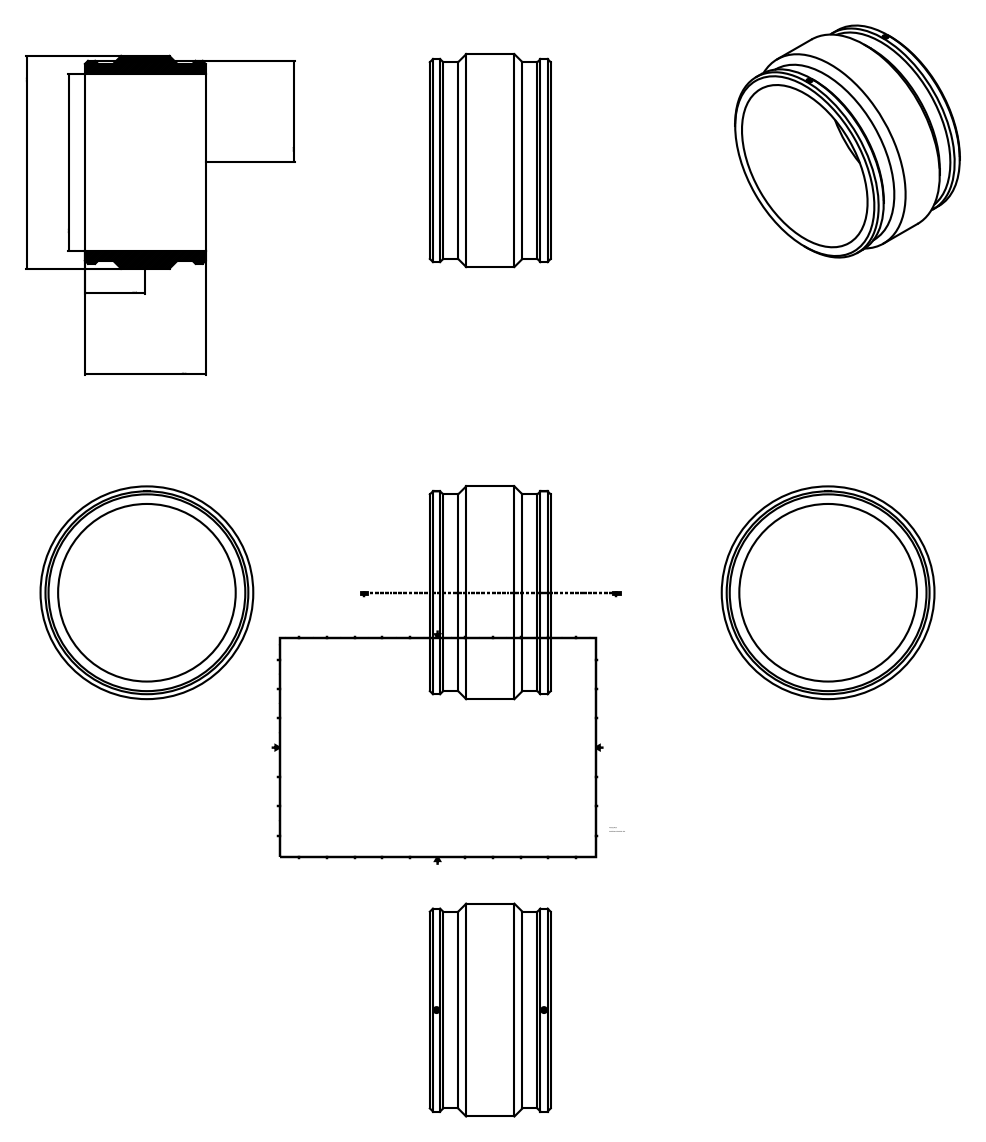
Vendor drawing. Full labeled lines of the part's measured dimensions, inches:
Part name (STEP PRODUCT): 490103450
STEP written by: Autodesk Inventor 2015 (AUTOMOTIVE_DESIGN)
Units: inches
Bodies: 1 solid, 28 faces (8 planar, 14 cylindrical, 6 other)
Overall size (bounding box): 21.22 × 21.22 × 12.047
Volume: 1 001 in³ · Surface area: 1 634 in²
Round holes (diameter × count): ⌀0.394 ×2, ⌀17.717 ×1
Round bosses / shafts (diameter × count): ⌀0.591 ×2, ⌀0.157 ×2, ⌀21.22 ×1, ⌀20.236 ×1, ⌀19.629 ×1
Main face-to-face distances: 12.047, 0.551, 0.433, 0.118
Hole centre spacings: 10.722
